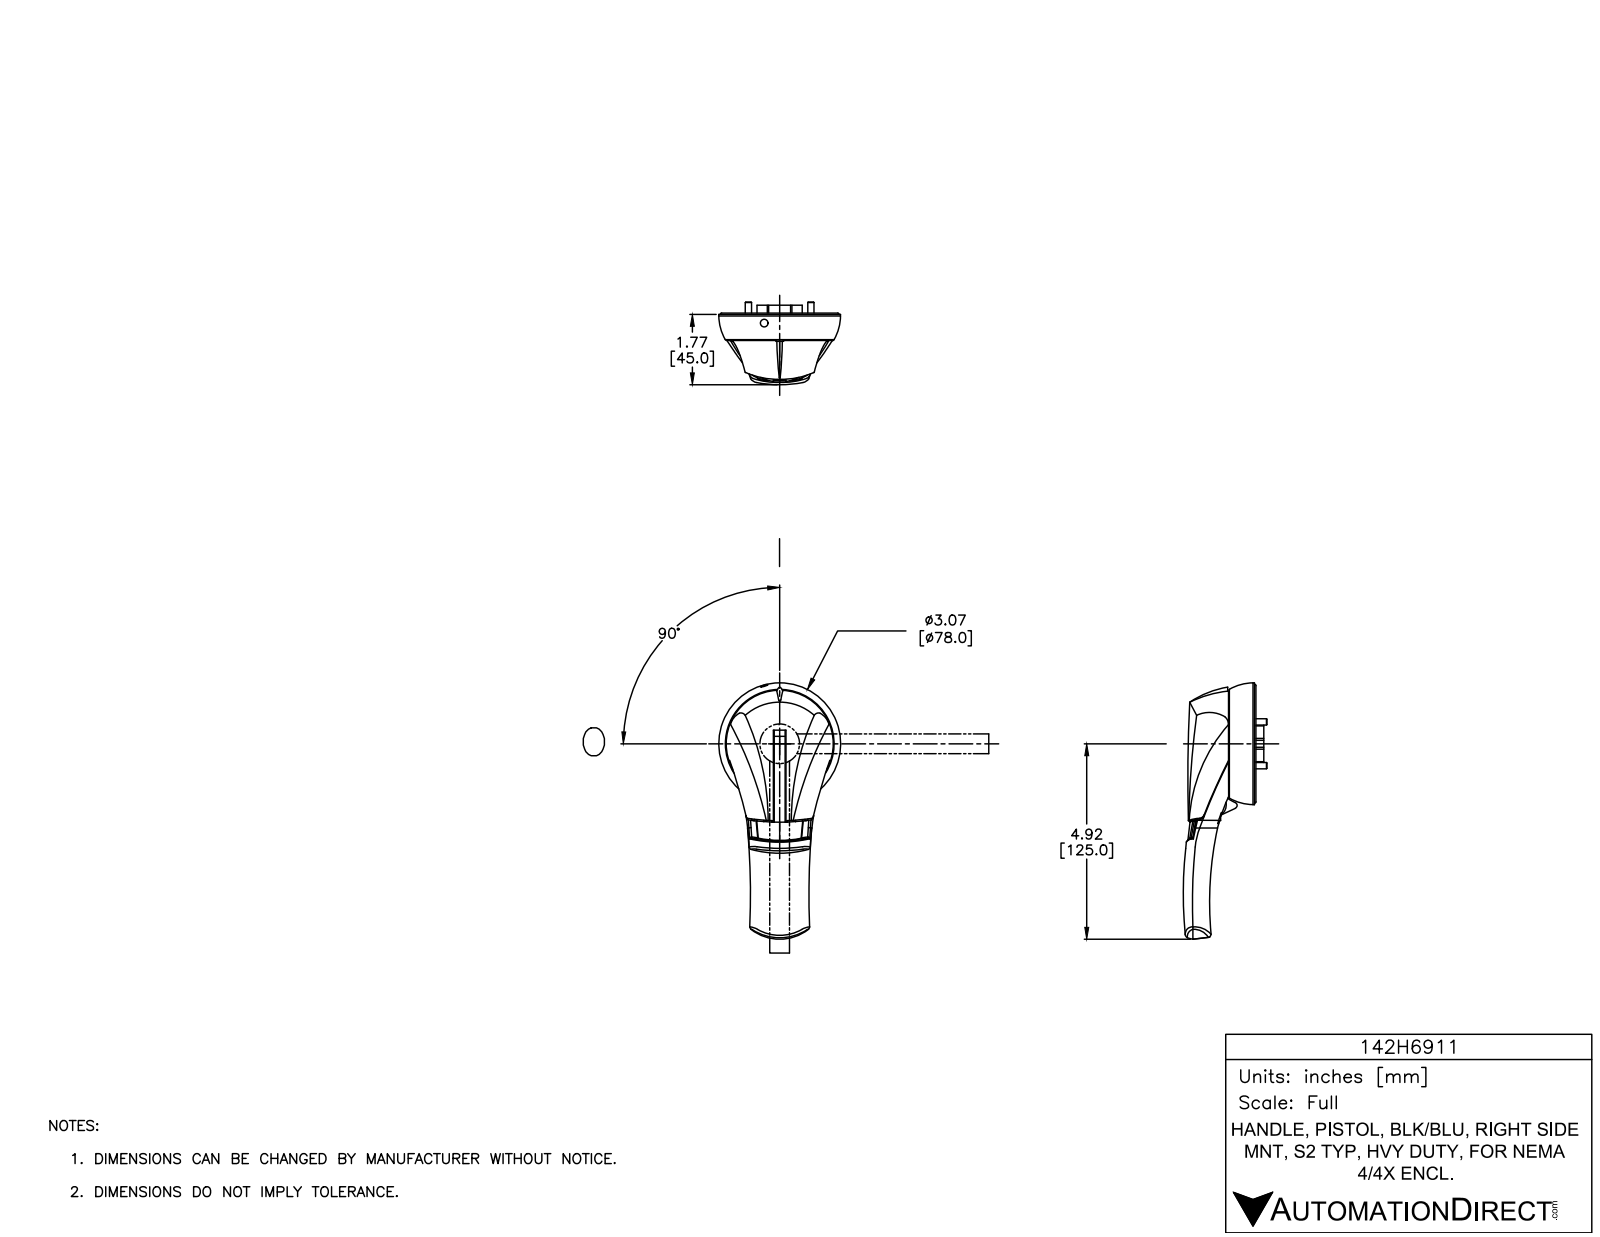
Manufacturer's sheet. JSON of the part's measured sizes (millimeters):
{"part_name": "142H6911", "step_written_by": "SolidWorks 2015 (AUTOMOTIVE_DESIGN)", "units": "millimeters", "bodies": {"solids": 8, "faces": 1516, "planar": 810, "cylindrical": 548, "other": 158}, "overall_size": [164, 78, 52.8], "volume_mm3": 155900, "surface_area_mm2": 56340, "round_holes": [[4, 6], [8.6, 4], [10.8, 4], [0.8, 3], [4.3, 2], [9.2, 2], [3, 1], [4.8, 1], [76, 1]], "round_bosses_or_shafts": [[0.5, 11], [8.5, 4], [8, 4], [2.3, 3], [1.8, 3], [5.8, 2], [71.6, 1], [68.6, 1]], "partial_cylinders_radius": [[0.3, 221], [0.4, 20], [0.9, 20], [0.8, 15], [1, 4], [0.6, 3], [138.1, 3], [2, 2]], "face_to_face_distances": [0.6, 17.8, 18.1, 17.5, 0.9, 2.6, 7, 4.4, 6.2, 1.2], "hole_center_spacings": [24.4, 7.8, 17, 27.9, 28, 30.6, 40, 47.8]}
